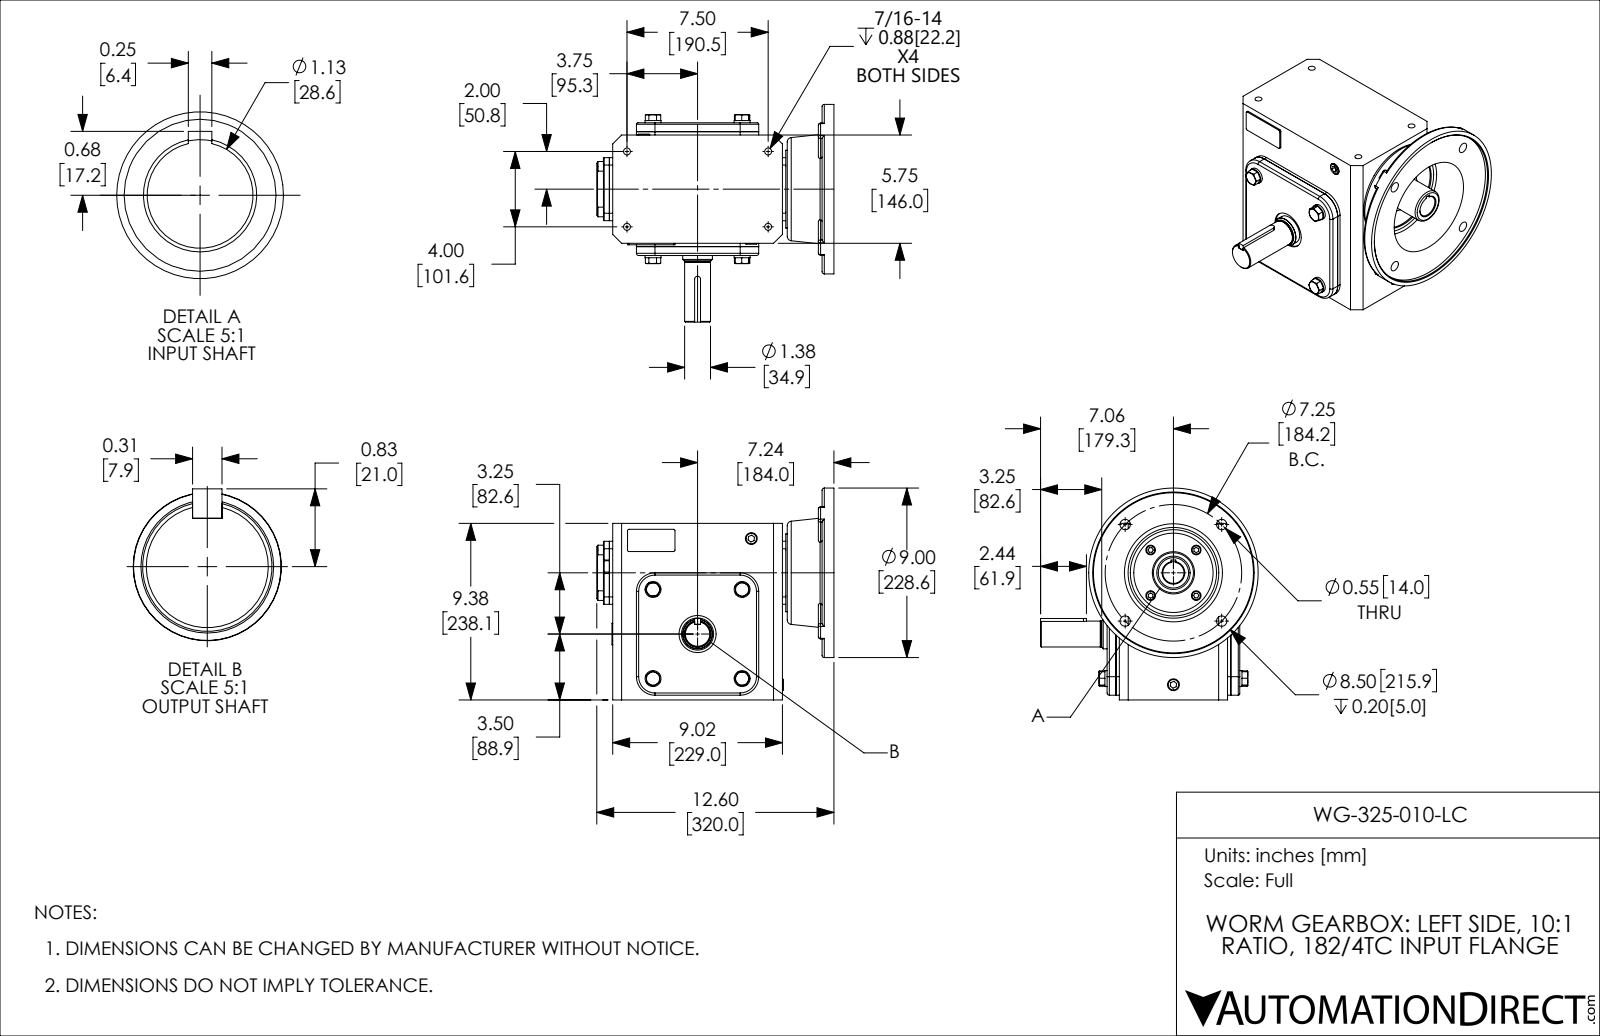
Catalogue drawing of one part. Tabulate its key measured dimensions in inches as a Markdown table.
| quantity | value |
| --- | --- |
| part name | WG-325-010-LC |
| STEP written by | SolidWorks 2017 (AUTOMOTIVE_DESIGN) |
| units | inches |
| bodies | 40 solids, 653 faces (336 planar, 195 cylindrical, 122 other) |
| overall size | 12.598 × 11.559 × 11.25 |
| volume | 529.7 in³ |
| surface area | 1 026 in² |
| round holes (diameter × count) | 0.354 × 4, 0.368 × 4, 0.551 × 4, 0.628 × 3, 0.591 × 1, 0.978 × 1, 1.125 × 1, 1.181 × 1, 1.969 × 1, 2.244 × 1, 2.441 × 1, 2.756 × 1 |
| round bosses / shafts (diameter × count) | 0.846 × 4, 0.512 × 4, 9 × 1, 4.134 × 1, 2.835 × 1, 1.772 × 1, 1.575 × 1, 1.375 × 1 |
| partial cylindrical surfaces (radius × count) | 0.118 × 14, 0.079 × 11, 0.394 × 4, 0.906 × 4, 0.984 × 4, 0.02 × 2, 0.039 × 2, 0.156 × 1 |
| main face-to-face distances | 0.079, 0.177, 6.496, 0.394, 6.969, 0.472, 6.575, 6.398, 0.571, 0.65 |
| hole center spacings | 4.009, 1.713, 1.913, 2.422, 3.625, 5.127, 5.338, 2.372 |
